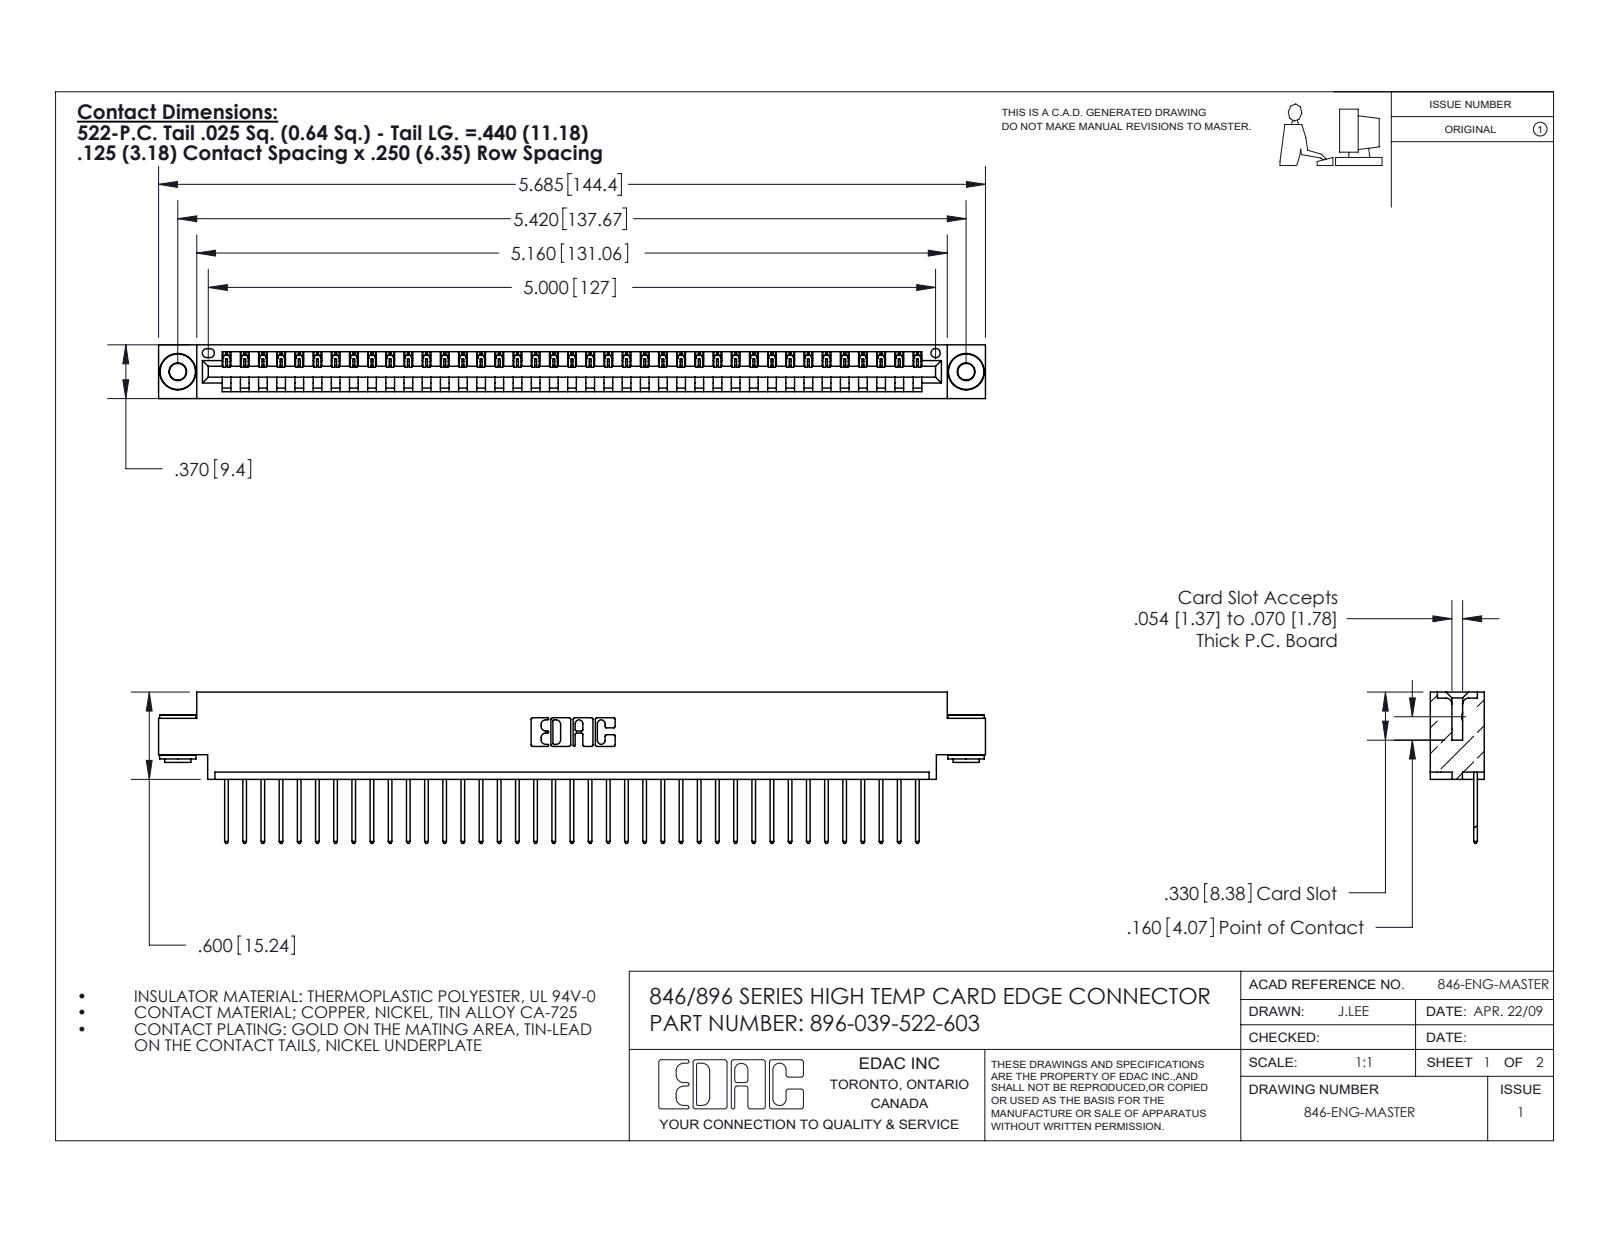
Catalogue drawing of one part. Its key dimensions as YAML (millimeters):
part_name: "345-250-002_345-250-002-102; 396-039-522-603; 346 Part_0.170 Offset - 0.156 Dia-TH; 345-292-001_345-293-122"
step_written_by: "SolidWorks 2016 (CONFIG_CONTROL_DESIGN)"
units: millimeters
bodies: {solids: 42, faces: 2426, planar: 1650, cylindrical: 768, other: 8}
overall_size: [144.4, 26.4, 9.4]
volume: 13700
surface_area: 17580
round_holes:
  - {diameter: 2.9, count: 2}
  - {diameter: 4, count: 2}
  - {diameter: 1.6, count: 1}
round_bosses_or_shafts:
  - {diameter: 6.4, count: 2}
  - {diameter: 4.6, count: 2}
  - {diameter: 3.5, count: 2}
partial_cylinders:
  - {radius: 0.2, count: 78}
  - {radius: 0.3, count: 78}
  - {radius: 0.3, count: 22}
  - {radius: 0.2, count: 6}
  - {radius: 0.8, count: 6}
  - {radius: 0.7, count: 3}
  - {radius: 0.8, count: 2}
  - {radius: 1, count: 2}
face_to_face_distances: [1.2, 8.2, 9.4, 6.4, 0.6, 1.8, 7.6, 3.8, 5.6, 2.5]
hole_center_spacings: [6.2, 132.4, 137.7]
